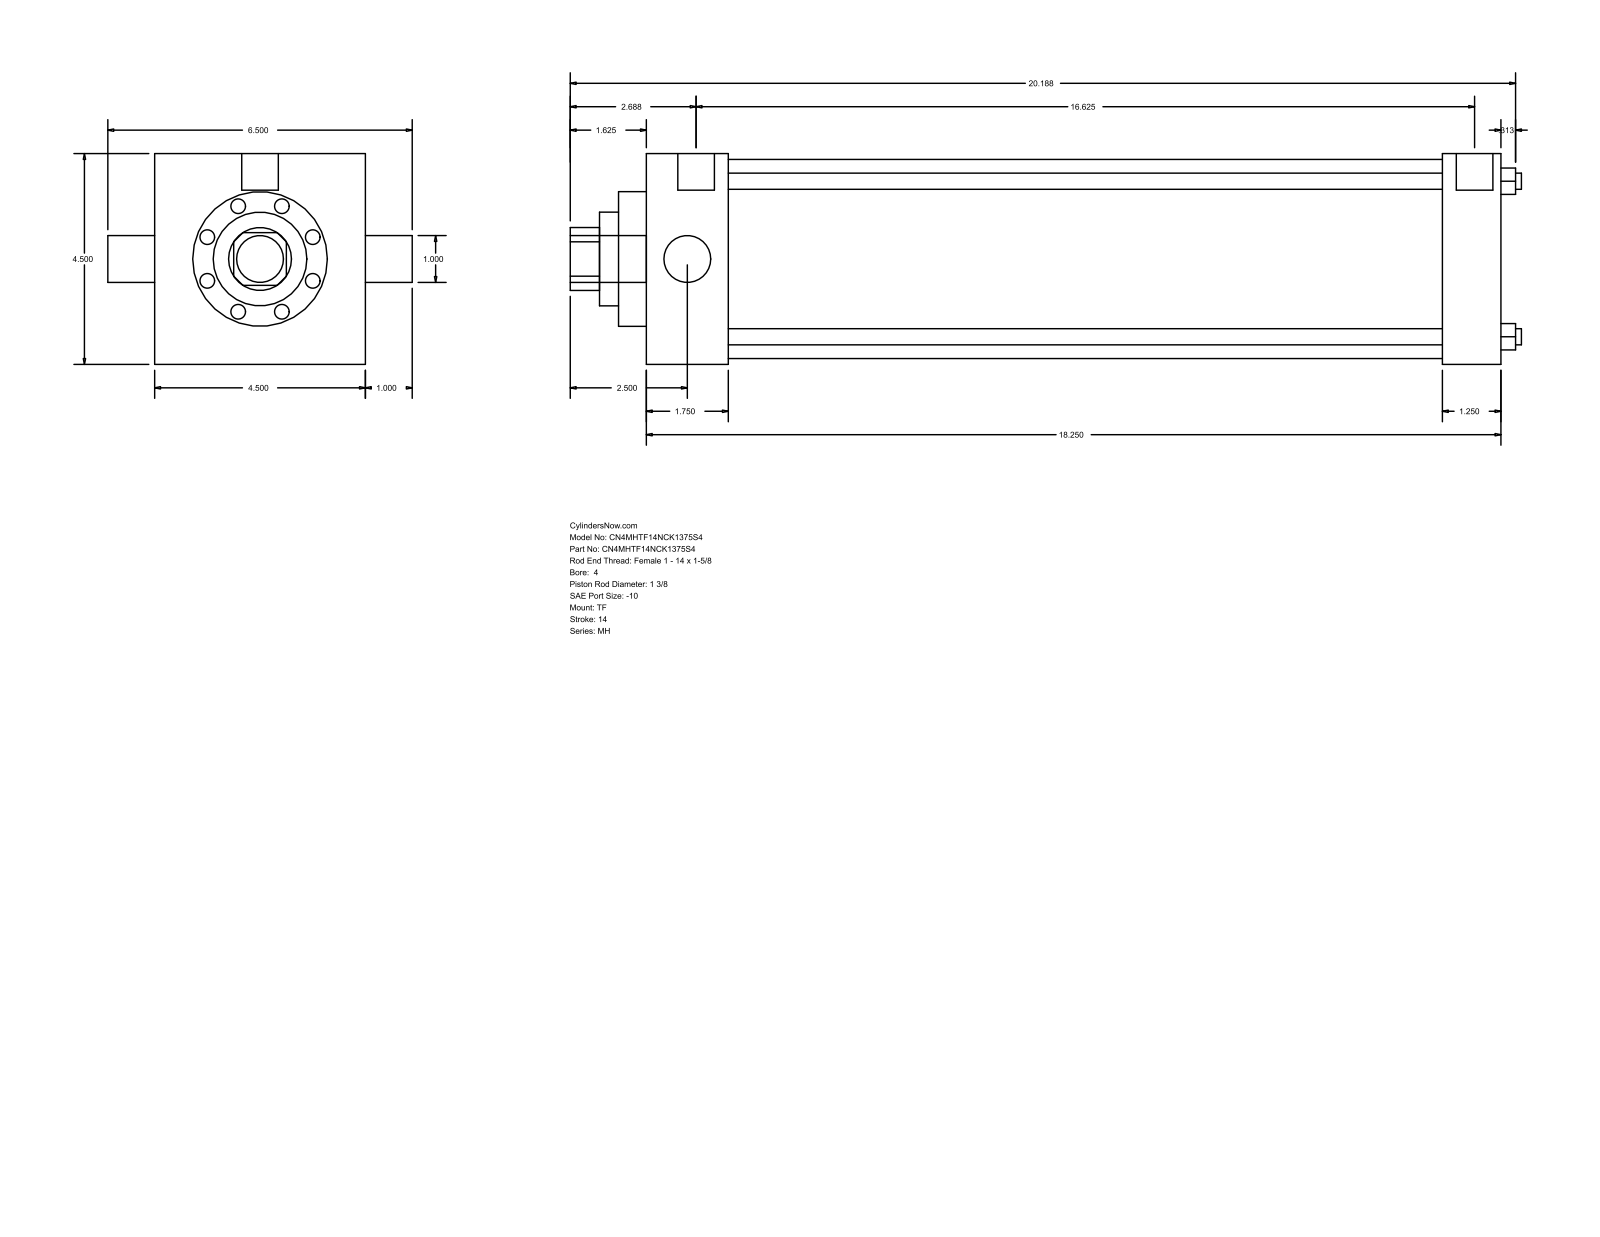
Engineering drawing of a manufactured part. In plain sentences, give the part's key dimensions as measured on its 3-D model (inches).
The part is named "MH_TF__0400_1.375". Its 3-D file was written by "GSSL Pune (CONFIG_CONTROL_DESIGN)". It is 0 solids with 86 faces: 61 planar, 25 cylindrical and 0 other. Overall it measures 20.313 by 6.5 by 4.5 inches. Round holes: 4 of diameter 0.345, 1 of diameter 1, 1 of diameter 1.375, 1 of diameter 2, 1 of diameter 2.875, 1 of diameter 4.25. Round bosses or shafts: 3 of diameter 0.344, 2 of diameter 0.781, 1 of diameter 1. Partial cylindrical surfaces (rounded edges, fillets, slot ends): 1 of radius 0.672. The main face-to-face distances are 4.5, 18.25, 1.75, 16.5, 17, 15.25, 1.25, 0.594, 2.344, 17.594. The hole center spacings are 2.347, 3.32, 4.695.
